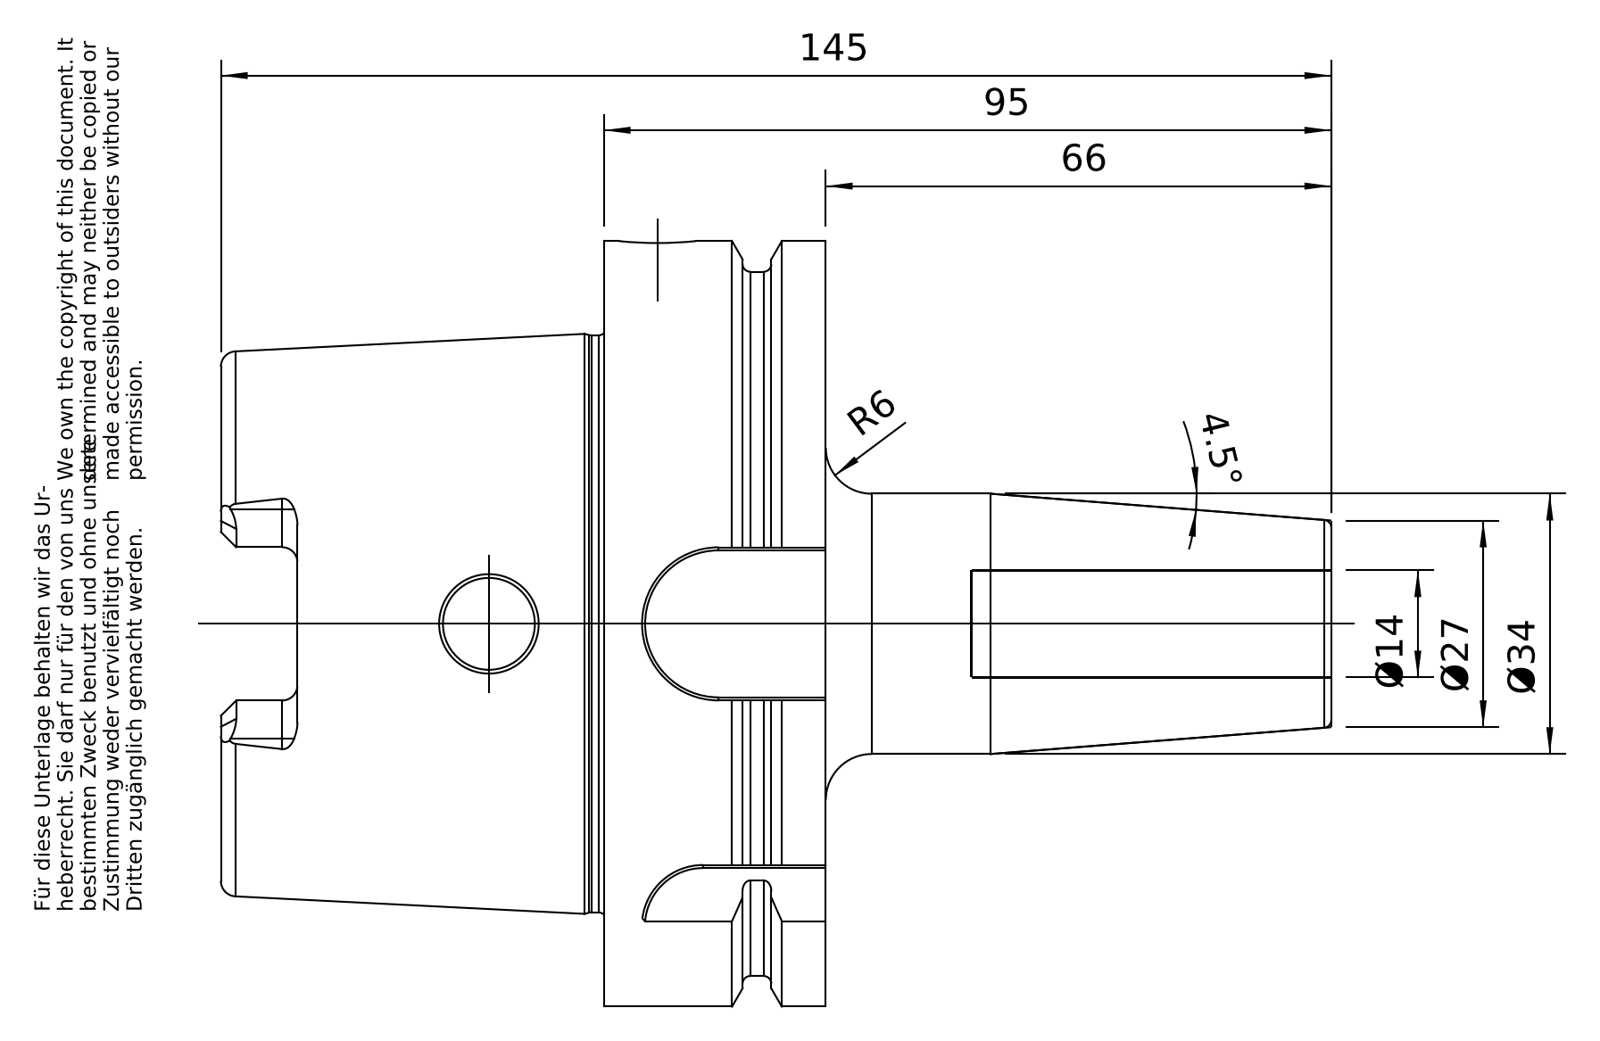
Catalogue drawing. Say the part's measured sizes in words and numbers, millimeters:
The part is named "A100-140-14". Its 3-D file was written by "PRO/ENGINEER BY PARAMETRIC TECHNOLOGY CORPORATION, 2010430 (CONFIG_CONTROL_DESIGN)". It is 1 solid with 174 faces: 50 planar, 51 cylindrical and 73 other. Overall it measures 145 by 100 by 100 millimeters. Its volume is 300 031 cubic millimeters and its surface area 58 252 square millimeters. Round holes: 1 of diameter 10, 1 of diameter 12, 1 of diameter 14, 1 of diameter 22.5, 1 of diameter 24, 1 of diameter 24.32, 1 of diameter 24.5, 1 of diameter 53, 1 of diameter 63. Round bosses or shafts: 1 of diameter 100, 1 of diameter 92, 1 of diameter 75.36, 1 of diameter 34. Partial cylindrical surfaces (rounded edges, fillets, slot ends): 6 of radius 2, 4 of radius 5, 1 of radius 8, 1 of radius 10, 1 of radius 11. The main face-to-face distances are 29, 12.5, 16.5, 50, 62.5, 79, 88, 78.5, 28.5, 16.
